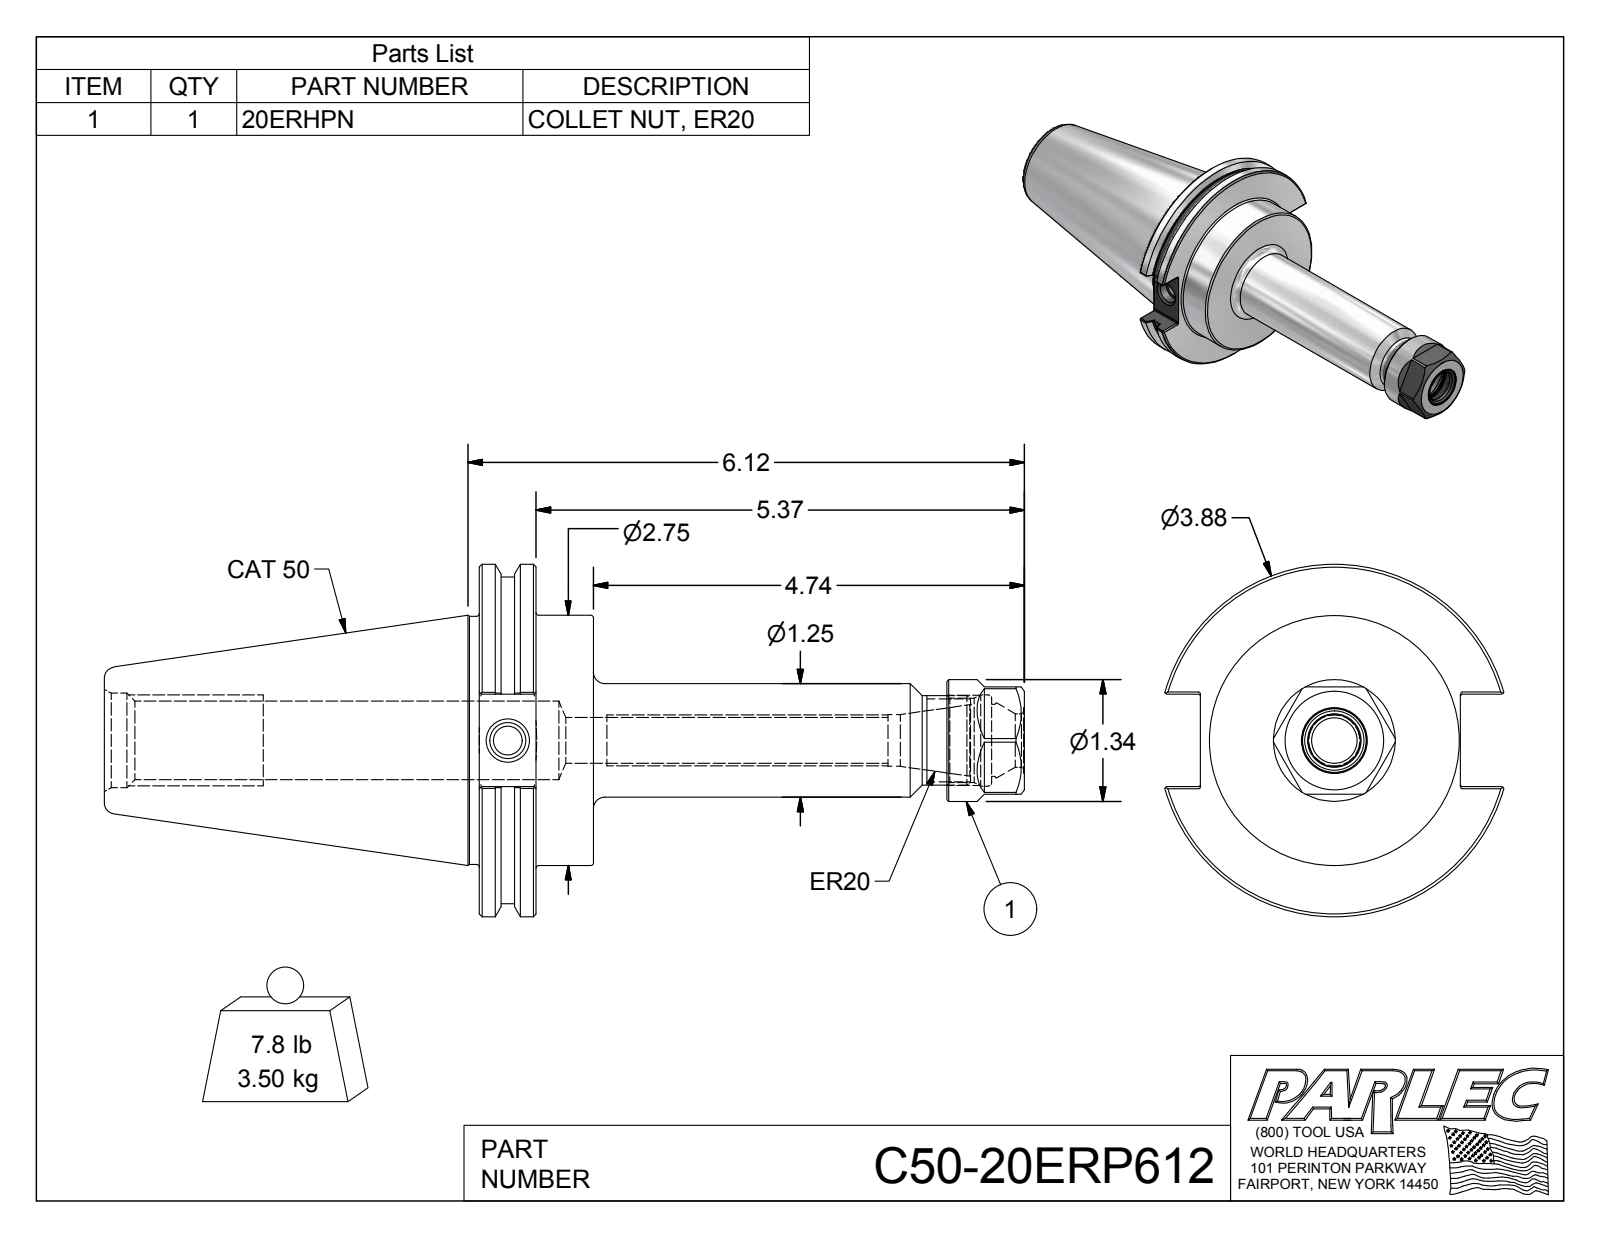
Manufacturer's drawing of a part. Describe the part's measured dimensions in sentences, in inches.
The part is named "C50-20ERP612; C50-20ER6-1; 20ERHPN". Its 3-D file was written by "Autodesk Inventor 2012 (AUTOMOTIVE_DESIGN)". It is 2 solids with 126 faces: 49 planar, 33 cylindrical and 44 other. Overall it measures 10.12 by 3.875 by 3.729 inches. Its volume is 27.35 cubic inches and its surface area 104.8 square inches. Round holes: 1 of diameter 0.315, 1 of diameter 0.399, 1 of diameter 0.502, 1 of diameter 0.57, 1 of diameter 0.587, 1 of diameter 0.79, 1 of diameter 0.865, 1 of diameter 0.926, 1 of diameter 1.005, 1 of diameter 1.038. Round bosses or shafts: 1 of diameter 3.875, 1 of diameter 3.594, 1 of diameter 2.75, 1 of diameter 2.73, 1 of diameter 1.34, 1 of diameter 1.25, 1 of diameter 0.984. Partial cylindrical surfaces (rounded edges, fillets, slot ends): 12 of radius 0.02. The main face-to-face distances are 0.625, 1.255, 0.63, 1.18, 5.145, 4.52, 3.89, 5.995, 5.37, 4.74.
